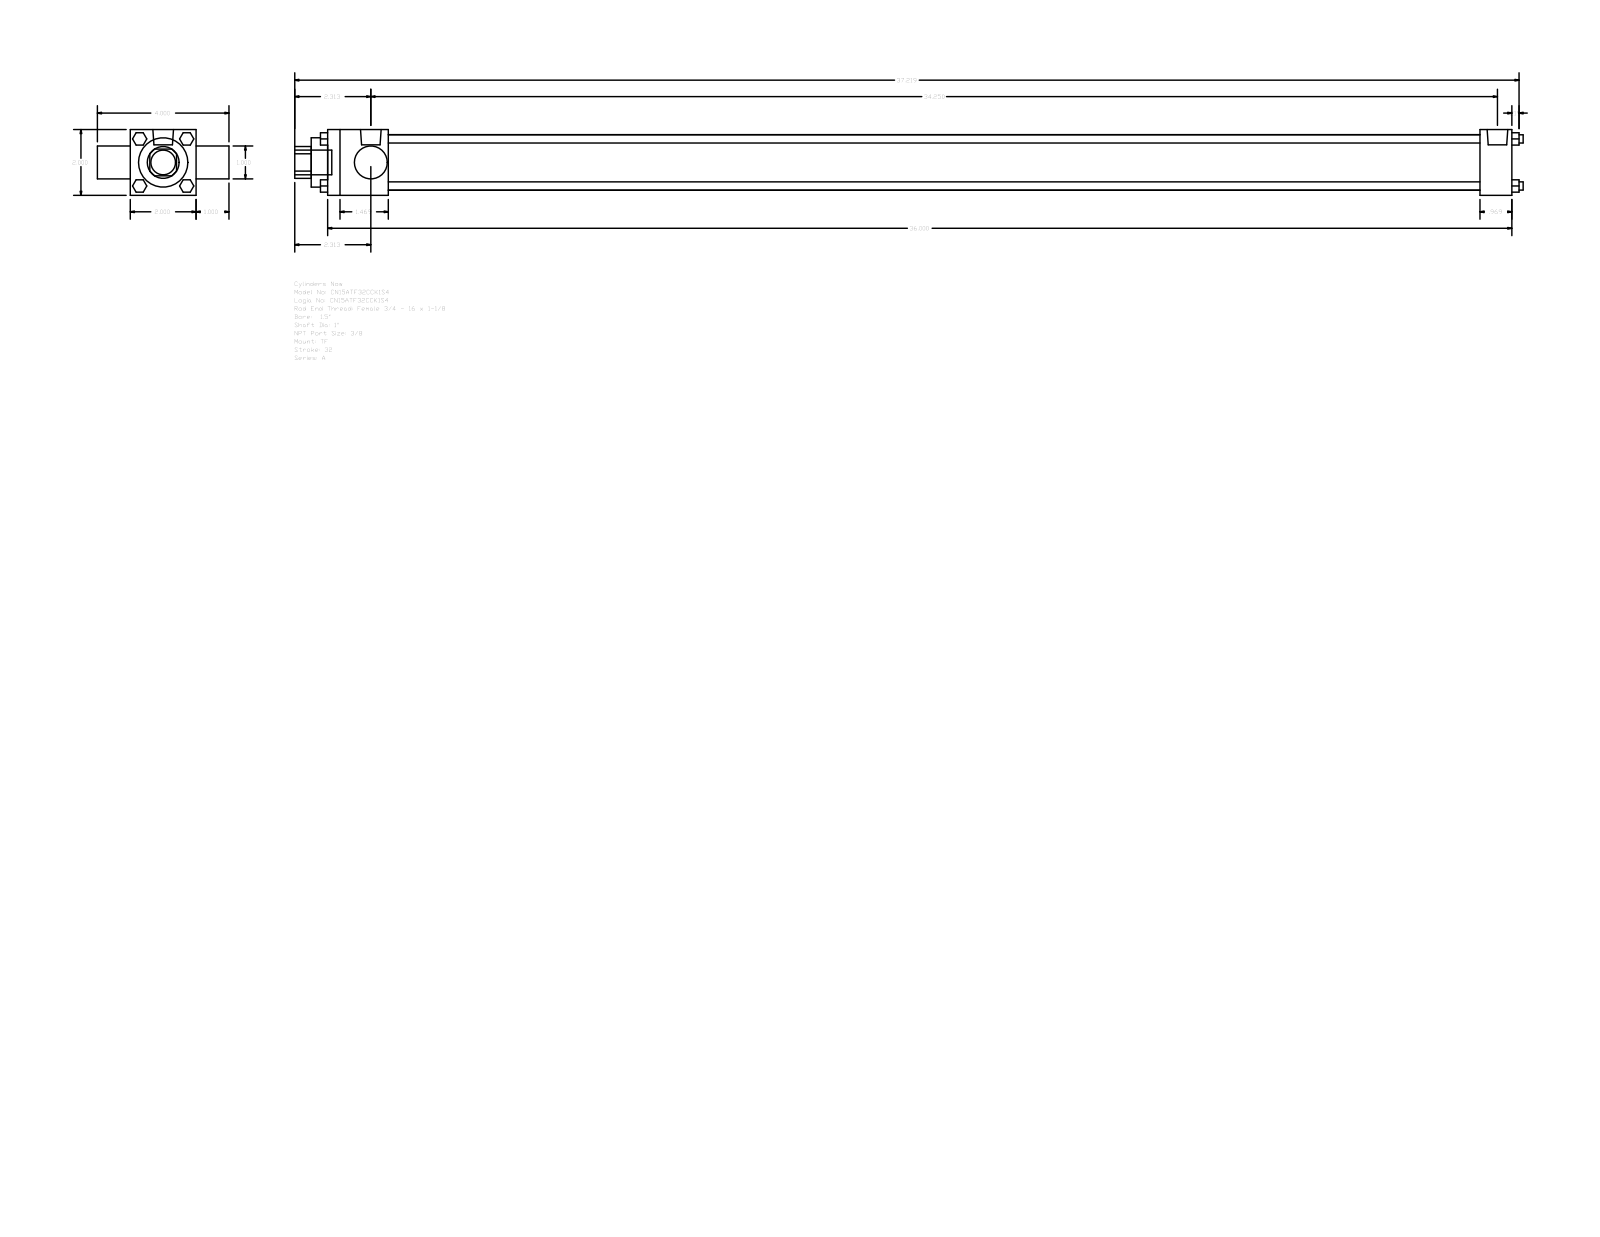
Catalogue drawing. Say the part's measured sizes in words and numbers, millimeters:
The part is named "A_TF__0150_1". Its 3-D file was written by "GSSL Pune (CONFIG_CONTROL_DESIGN)". It is 0 solids with 120 faces: 92 planar, 28 cylindrical and 0 other. Overall it measures 948.53 by 101.6 by 50.8 millimeters. Round holes: 2 of diameter 25.4, 1 of diameter 38.1, 1 of diameter 42.93. Round bosses or shafts: 4 of diameter 6.35, 3 of diameter 5.56, 2 of diameter 15.93, 1 of diameter 19.05. Partial cylindrical surfaces (rounded edges, fillets, slot ends): 1 of radius 12.29. The main face-to-face distances are 50.8, 25.4, 914.4, 76.2, 46.83, 889.79, 842.96, 867.57, 24.61, 12.7.
